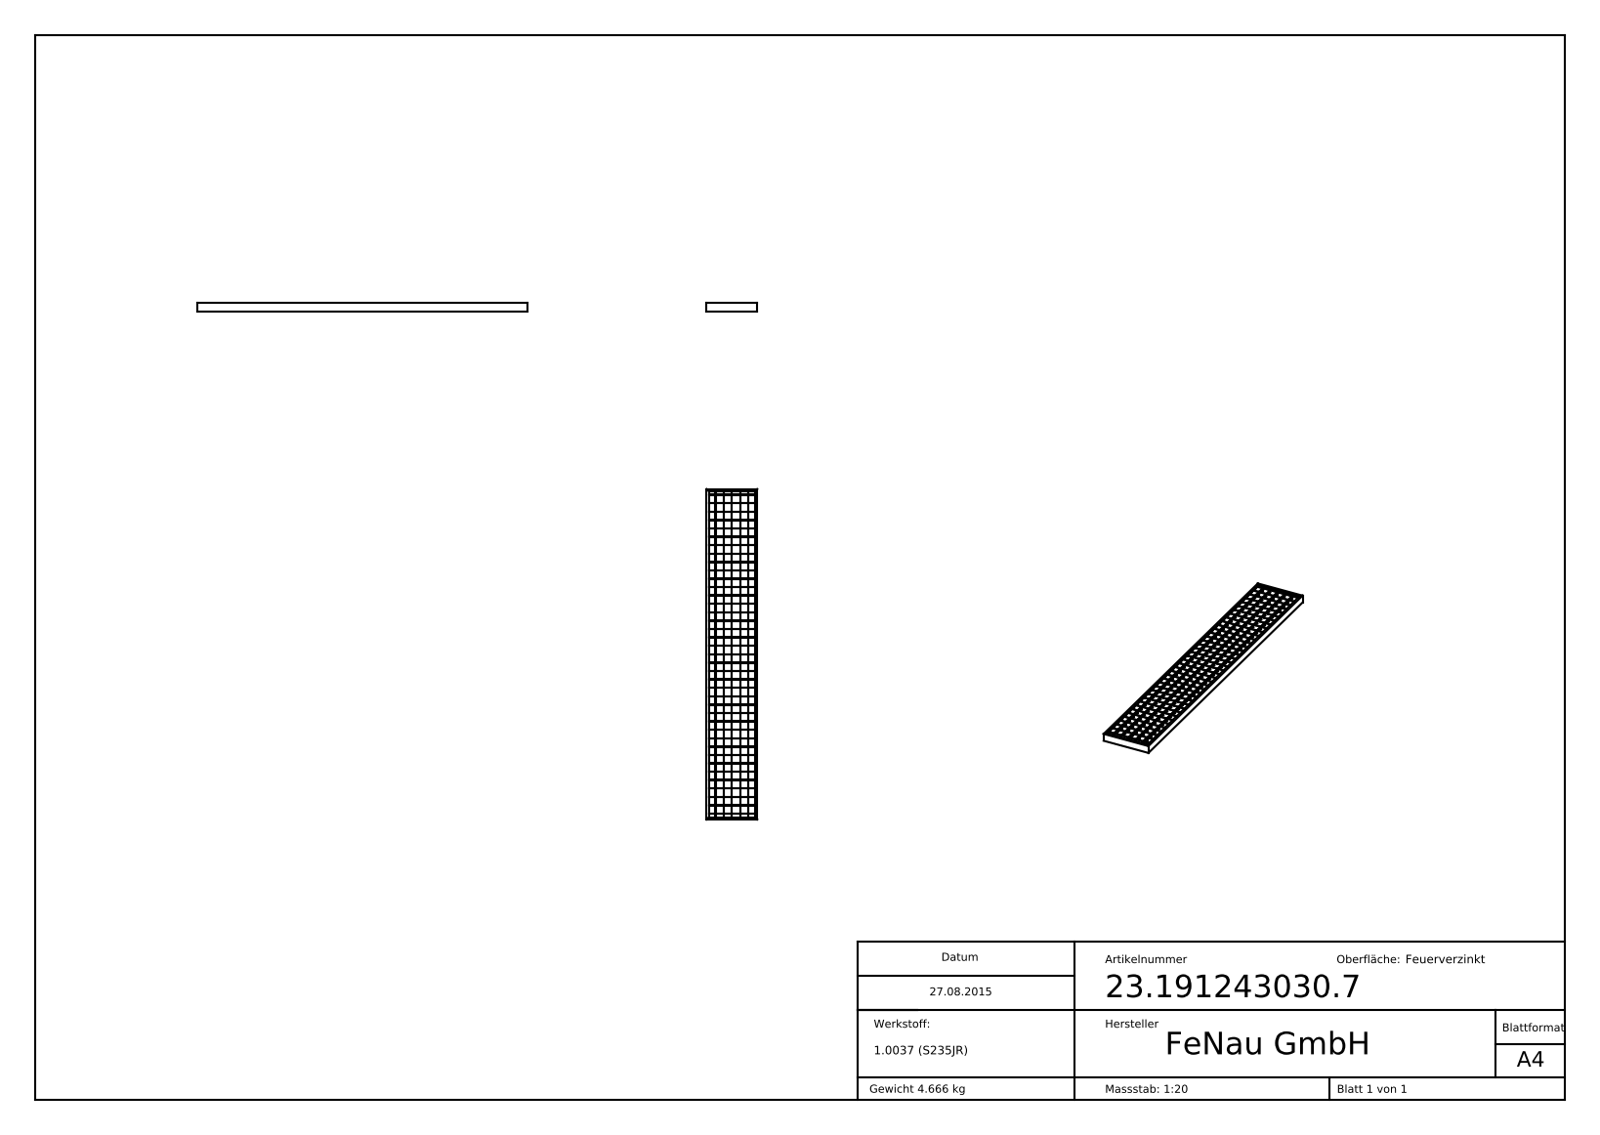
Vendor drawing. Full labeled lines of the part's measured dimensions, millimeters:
Part name (STEP PRODUCT): 23-191243030-7
STEP written by: SolidWorks 2015 (CONFIG_CONTROL_DESIGN)
Units: millimetres
Bodies: 1 solid, 1112 faces (1112 planar, 0 cylindrical, 0 other)
Overall size (bounding box): 1240 × 190 × 30
Volume: 598 161 mm³ · Surface area: 791 013 mm²
Main face-to-face distances: 63, 31.5, 31, 94.5, 157.5, 62, 30, 126, 189, 93
